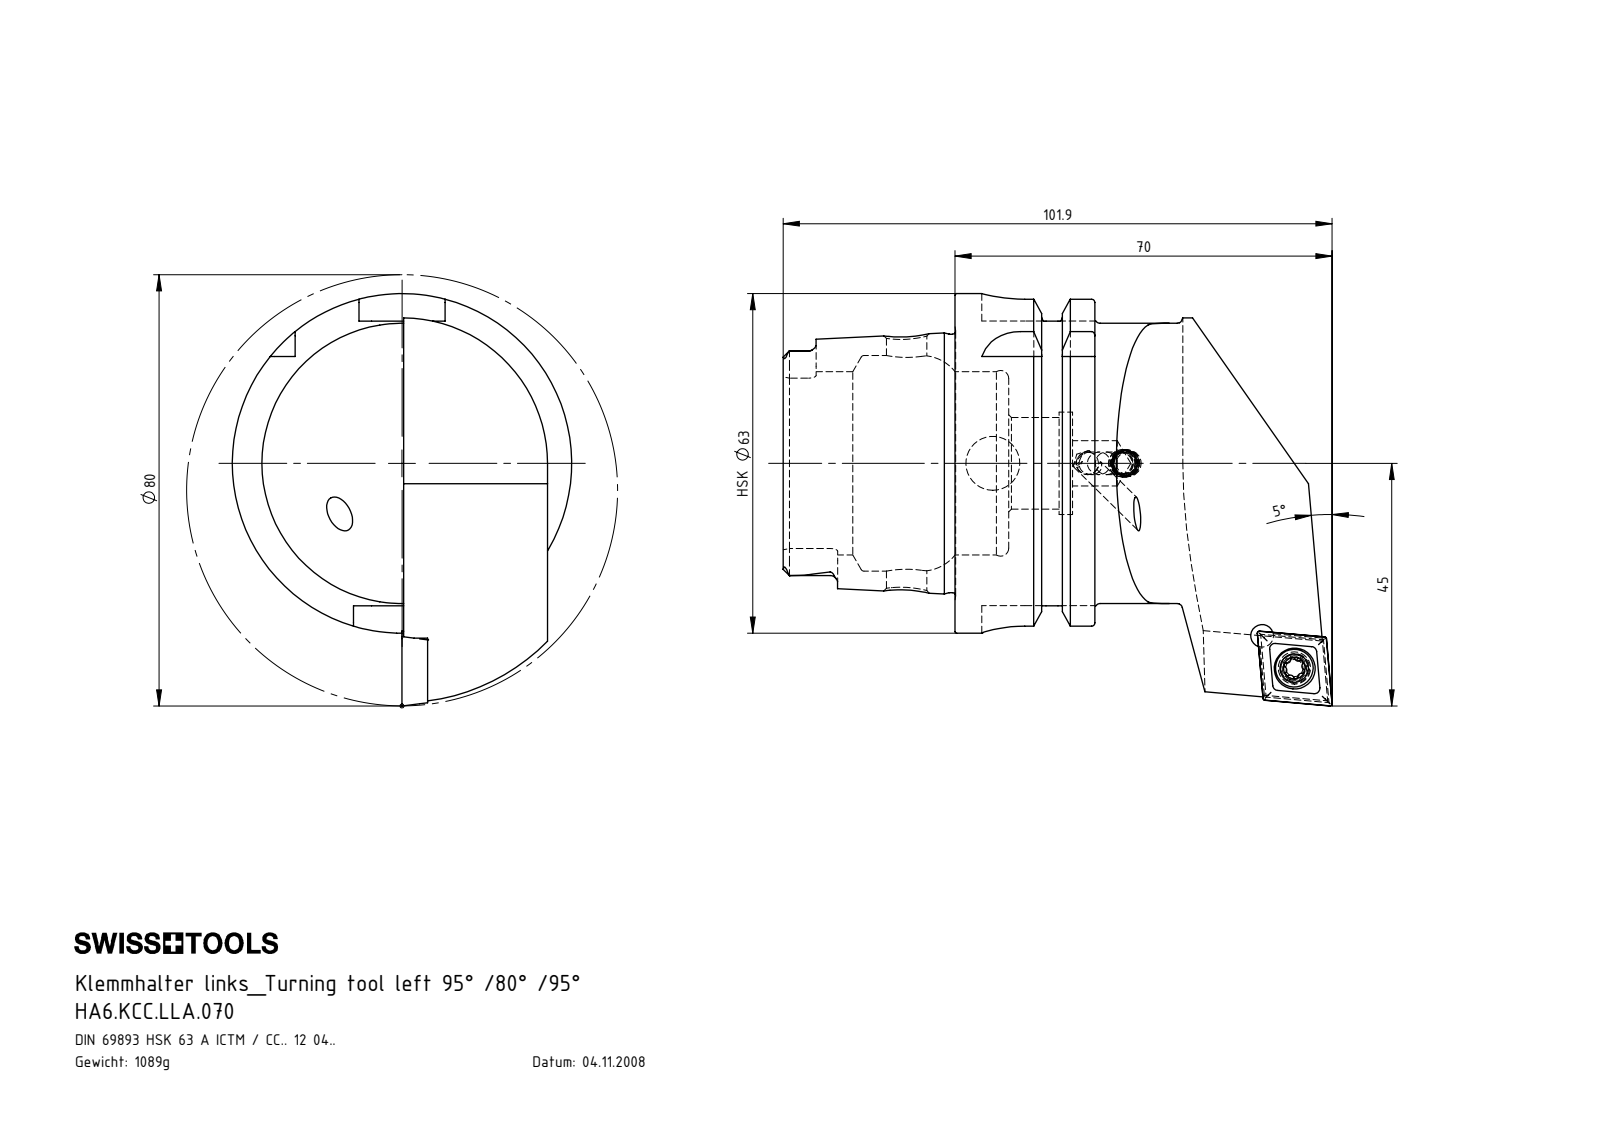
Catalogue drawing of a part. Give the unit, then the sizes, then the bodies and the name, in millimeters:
Units: millimetres
Overall size (bounding box): 101.9 × 76.5 × 63
Round holes (diameter × count): ⌀4.2 ×2, ⌀5 ×2, ⌀5.5 ×1, ⌀7.5 ×1, ⌀7.6 ×1, ⌀8.4 ×1, ⌀10 ×1, ⌀17 ×1, ⌀19 ×1, ⌀34 ×1, ⌀40 ×1
Round bosses / shafts (diameter × count): ⌀63 ×1, ⌀54.95 ×1, ⌀52 ×1, ⌀47.94 ×1, ⌀7 ×1, ⌀6 ×1, ⌀5 ×1
Partial cylindrical surfaces — rounded edges, fillets, slot ends (radius × count): R0.39 ×6, R1.4 ×6, R8 ×4, R0.69 ×3, R0.69 ×3, R2.82 ×2, R2.88 ×2, R6 ×1
Main face-to-face distances: 26.7, 25.95, 16, 9.95, 31.9, 41.85, 57.85, 52.8, 21.8, 11.85
Hole centre spacings: 8.3, 8.57, 59.35, 67.48, 67.75
Volume: 138 328 mm³ · Surface area: 30 873 mm²
Bodies: 5 solids, 230 faces (76 planar, 61 cylindrical, 93 other)
Part name (STEP PRODUCT): KVT_MB_600_060; HA6.KCC.LLA.070; CCMT120404; WCC-ER2.001.010_A (+1 more)
STEP written by: SolidWorks 2017 (AUTOMOTIVE_DESIGN)
